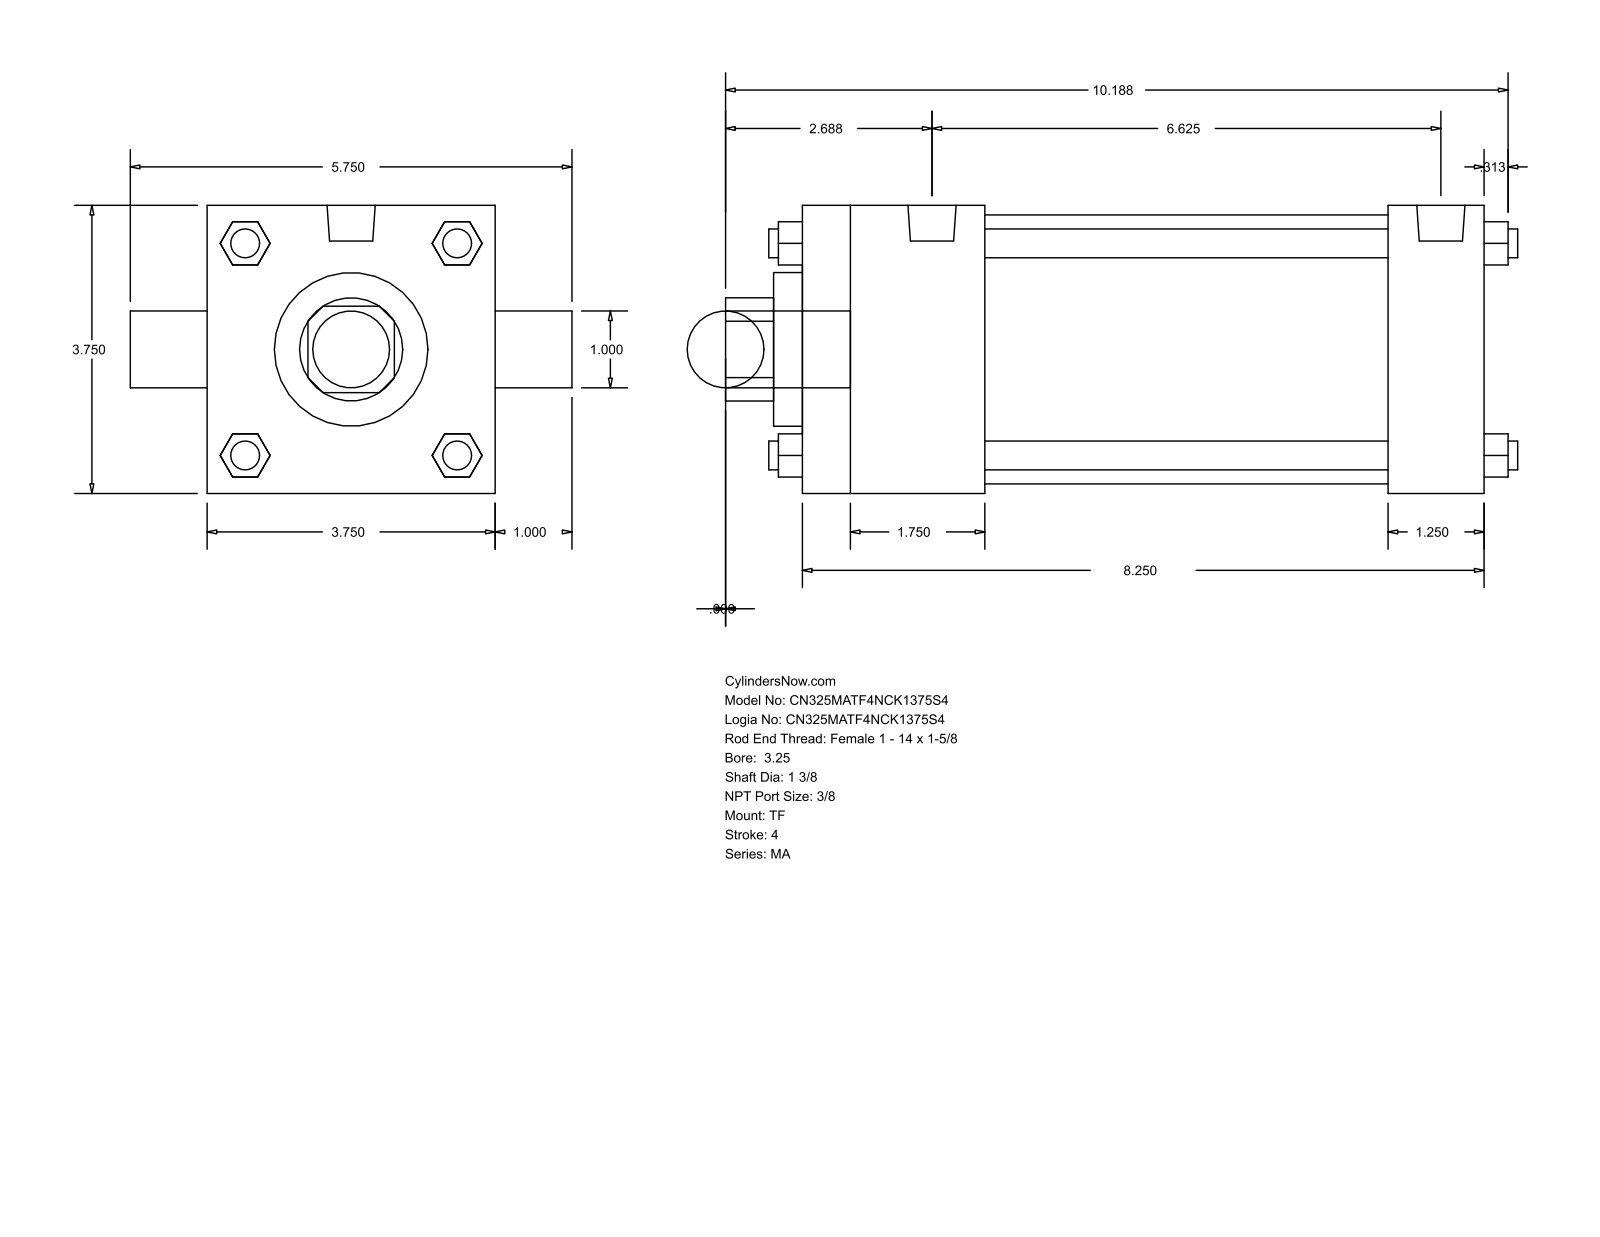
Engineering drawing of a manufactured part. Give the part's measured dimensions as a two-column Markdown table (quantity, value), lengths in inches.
| quantity | value |
| --- | --- |
| part name | MA_TF__0325_1.375 |
| STEP written by | GSSL Pune (CONFIG_CONTROL_DESIGN) |
| units | inches |
| bodies | 0 solids, 120 faces (92 planar, 28 cylindrical, 0 other) |
| overall size | 10.313 × 5.75 × 3.75 |
| round holes (diameter × count) | 1 × 1, 1.375 × 1, 2 × 1, 3.5 × 1 |
| round bosses / shafts (diameter × count) | 0.375 × 4, 0.437 × 3, 0.627 × 2, 1 × 1 |
| partial cylindrical surfaces (radius × count) | 0.672 × 1 |
| main face-to-face distances | 3.75, 8.875, 2.375, 7.625, 5.25, 6.5, 1.25, 0.375, 2.75, 8 |
